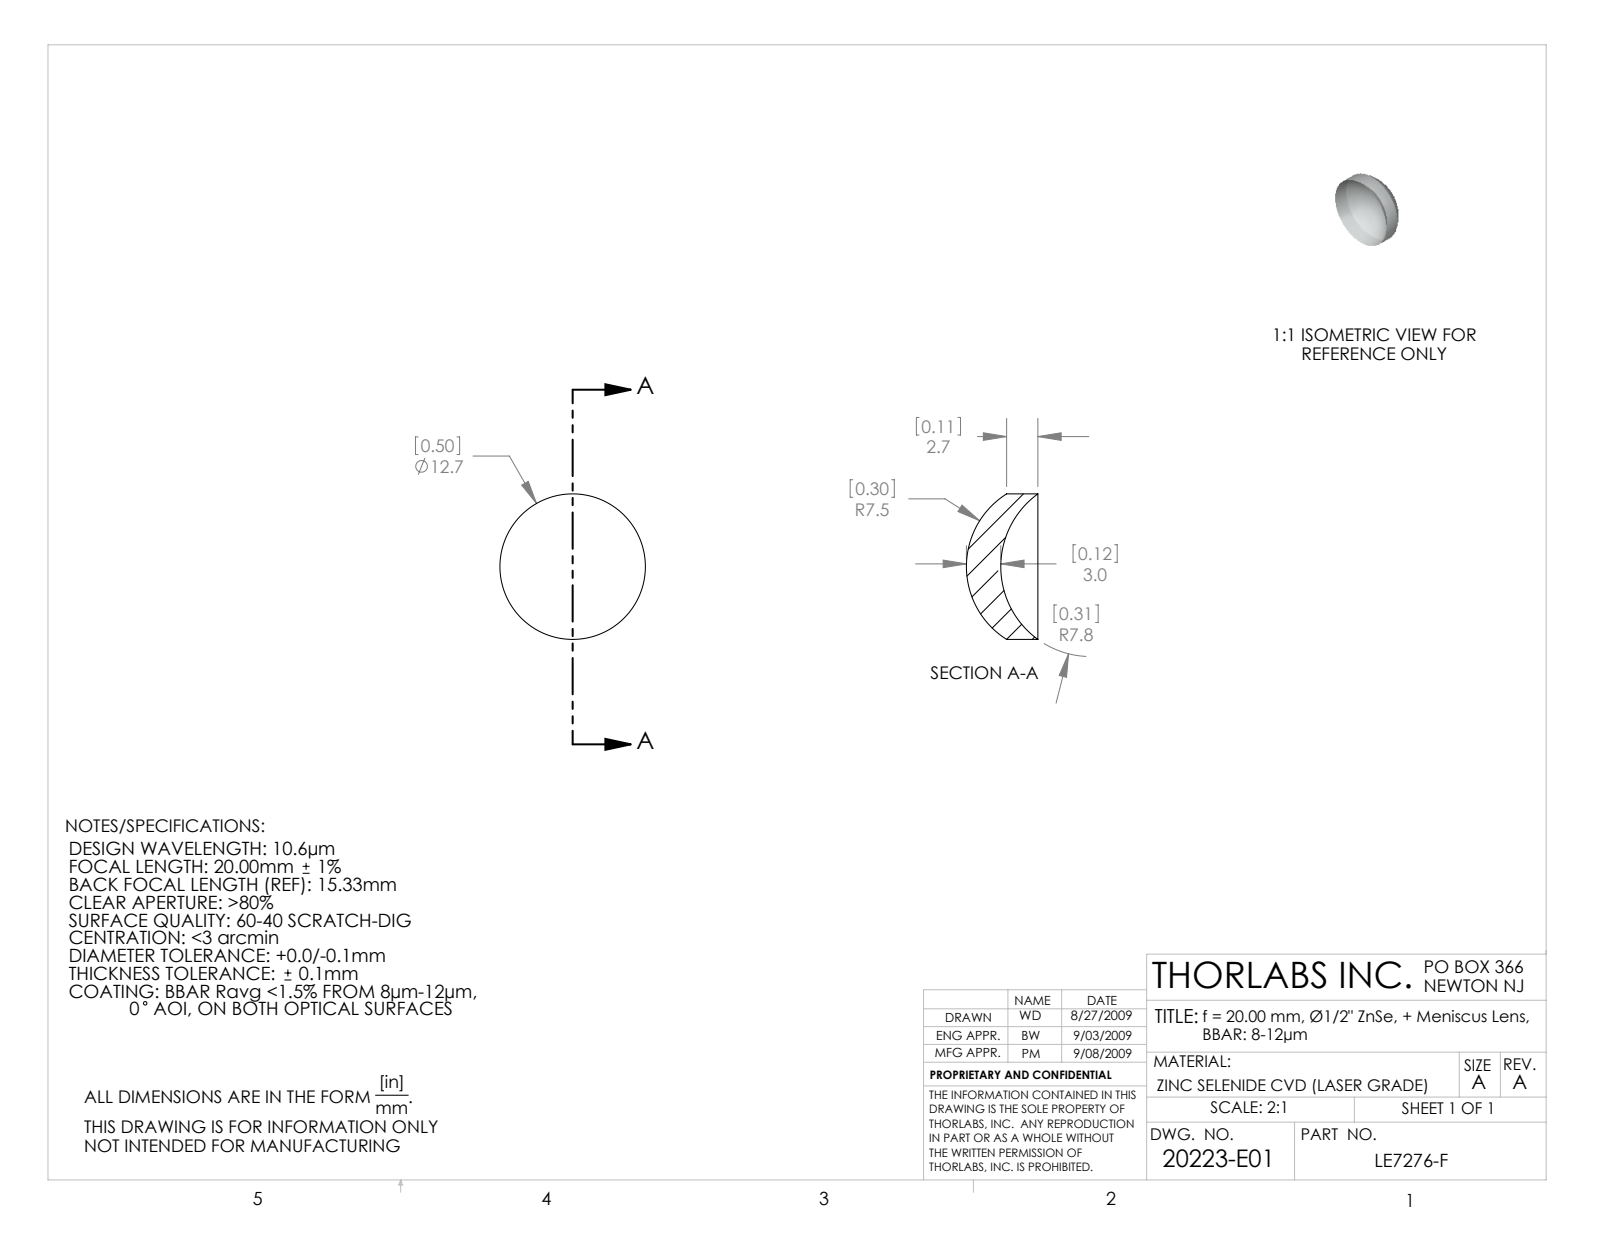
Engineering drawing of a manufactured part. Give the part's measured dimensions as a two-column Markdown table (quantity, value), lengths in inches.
| quantity | value |
| --- | --- |
| part name | 20223-E0W |
| STEP written by | SolidWorks 2007 (CONFIG_CONTROL_DESIGN) |
| units | inches |
| bodies | 1 solid, 6 faces (0 planar, 2 cylindrical, 4 other) |
| overall size | 0.5 × 0.5 × 0.246 |
| volume | 0.022 in³ |
| surface area | 0.673 in² |
| round bosses / shafts (diameter × count) | 0.5 × 1 |
